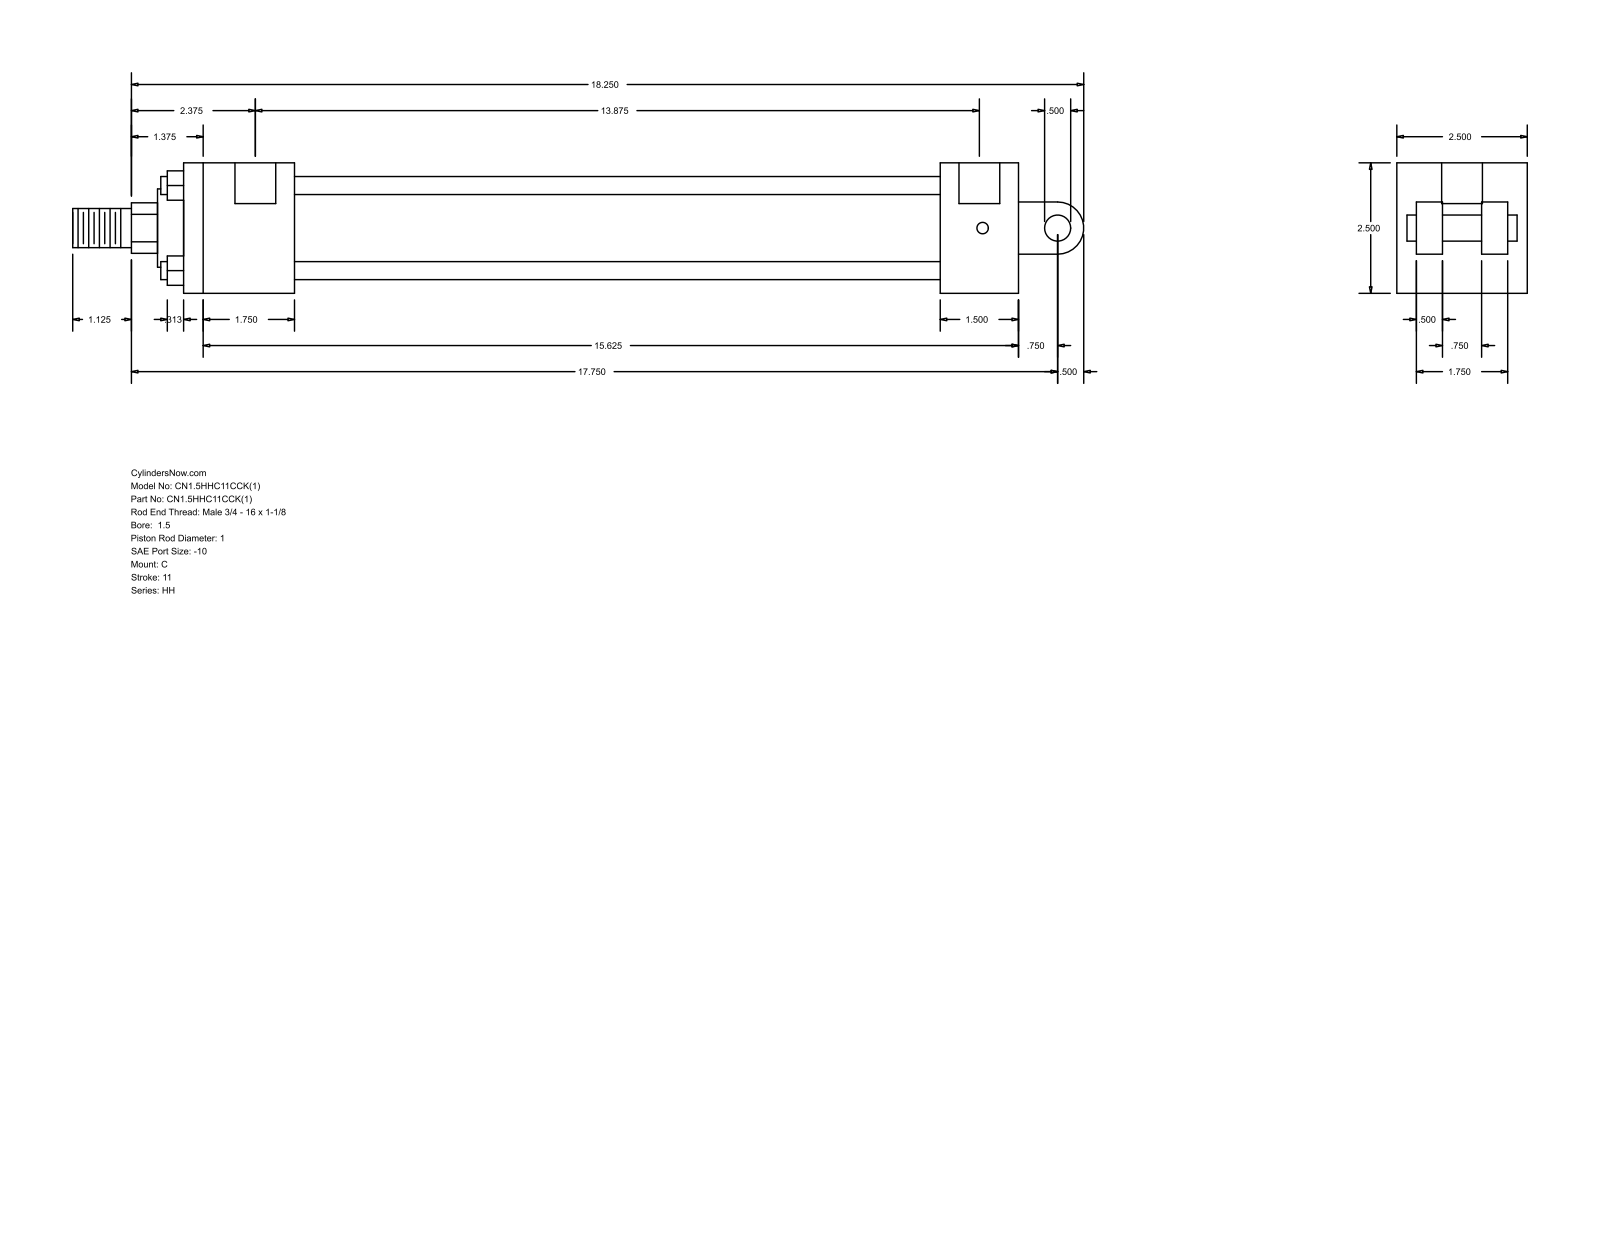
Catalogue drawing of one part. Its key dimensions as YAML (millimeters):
part_name: "HH_C__0150_1"
step_written_by: "GSSL Pune (CONFIG_CONTROL_DESIGN)"
units: millimeters
bodies: {solids: 0, faces: 99, planar: 70, cylindrical: 29, other: 0}
overall_size: [492.12, 63.5, 63.5]
round_holes:
  - {diameter: 5.56, count: 4}
  - {diameter: 19.84, count: 2}
round_bosses_or_shafts:
  - {diameter: 8.76, count: 4}
  - {diameter: 44.45, count: 1}
  - {diameter: 38.1, count: 1}
  - {diameter: 25.4, count: 1}
  - {diameter: 19.05, count: 1}
  - {diameter: 12.7, count: 1}
partial_cylinders:
  - {radius: 12.29, count: 1}
  - {radius: 12.7, count: 1}
face_to_face_distances: [63.5, 53.98, 38.1, 314.32, 352.42, 368.3, 406.4, 12.7, 22.22, 41.28]
hole_center_spacings: [1.59, 354.01, 355.6, 352.42]
